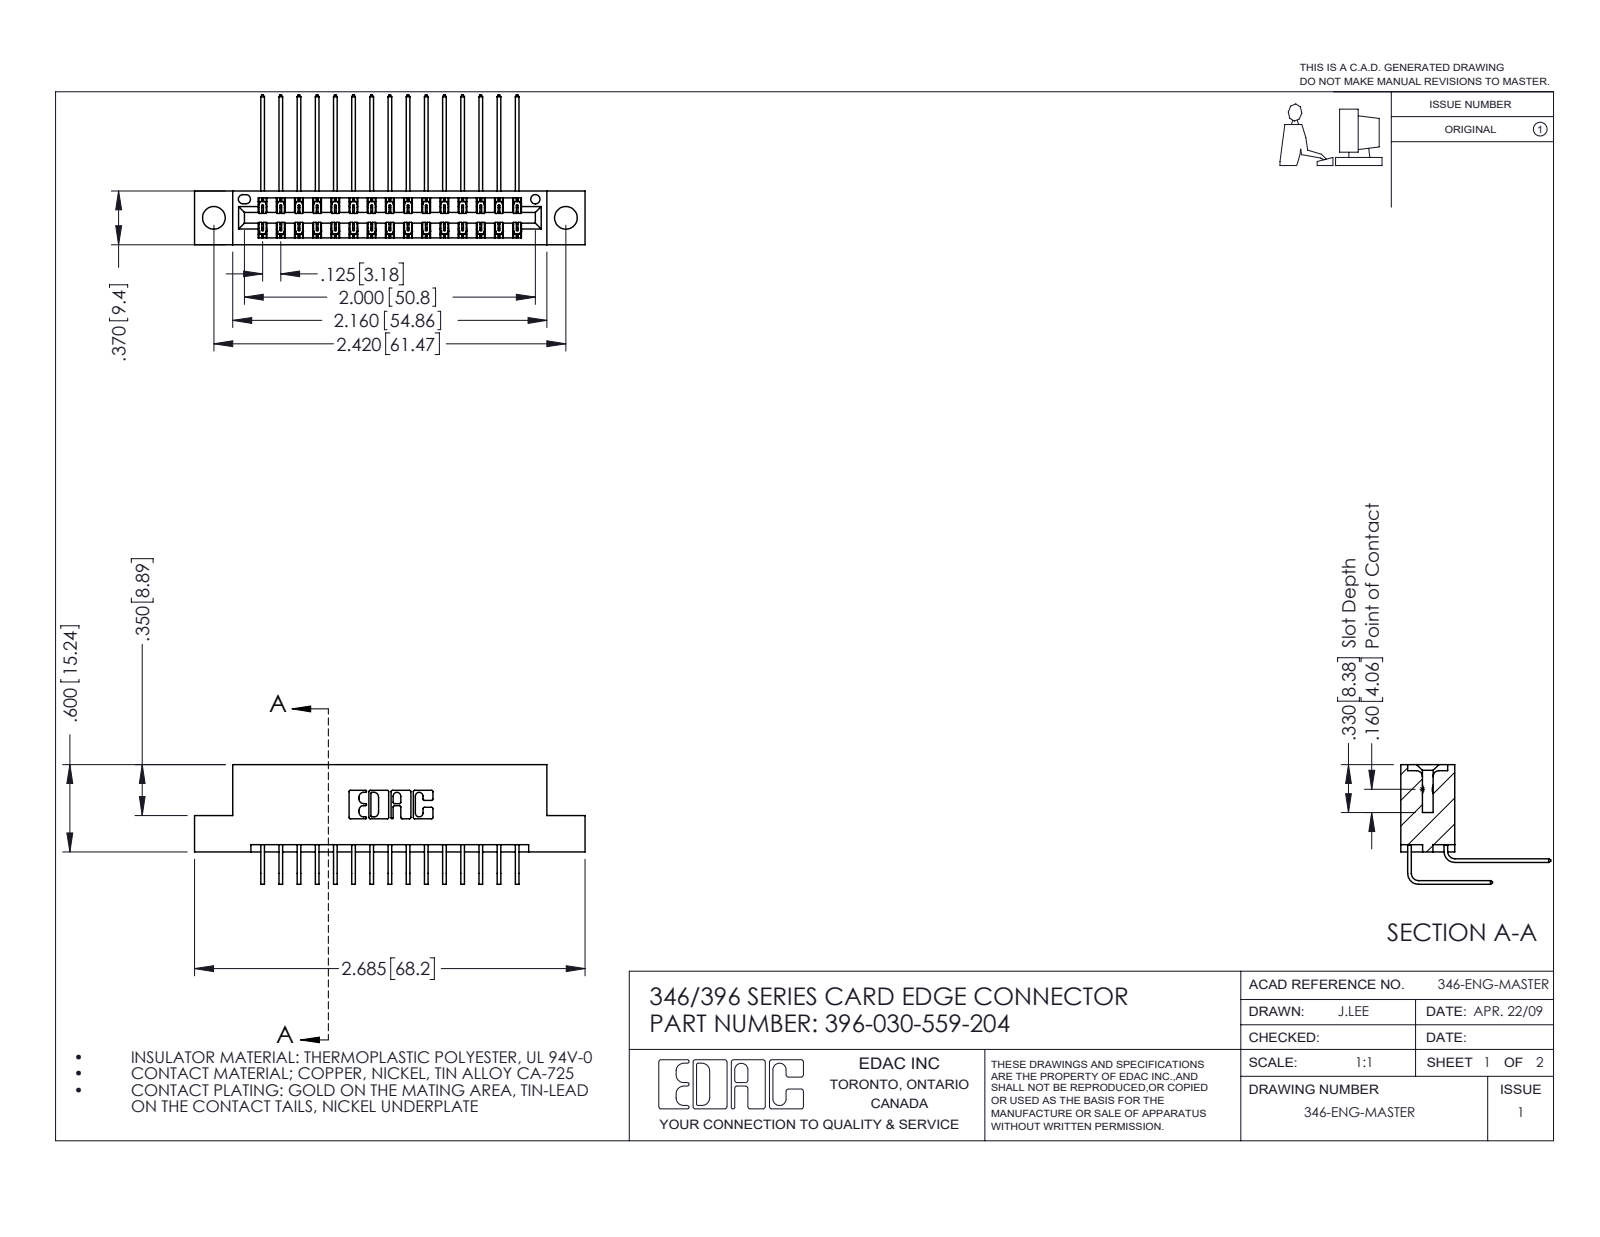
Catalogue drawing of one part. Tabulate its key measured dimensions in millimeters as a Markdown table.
| quantity | value |
| --- | --- |
| part name | 346 Part_Flush Mounting Lugs - 0.156 Dia-TH; 345-292-001_559 Tail - 2; 345-292-001_558 559 Tail - 1; 396-030-559-204 |
| STEP written by | SolidWorks 2016 (CONFIG_CONTROL_DESIGN) |
| units | millimeters |
| bodies | 31 solids, 1742 faces (1186 planar, 556 cylindrical, 0 other) |
| overall size | 68.2 × 26.2 × 20.9 |
| volume | 6 520 mm³ |
| surface area | 9 187 mm² |
| round holes (diameter × count) | 4 × 2, 1.6 × 1 |
| partial cylindrical surfaces (radius × count) | 0.2 × 45, 0.3 × 22, 0.2 × 6, 0.8 × 6, 0.7 × 3, 0.4 × 2, 0.6 × 2, 0.6 × 2 |
| main face-to-face distances | 1.2, 8.2, 6.4, 0.6, 9.4, 1.8, 7.6, 7, 3.8, 5.6 |
| hole center spacings | 6.2, 56.2, 61.5 |
